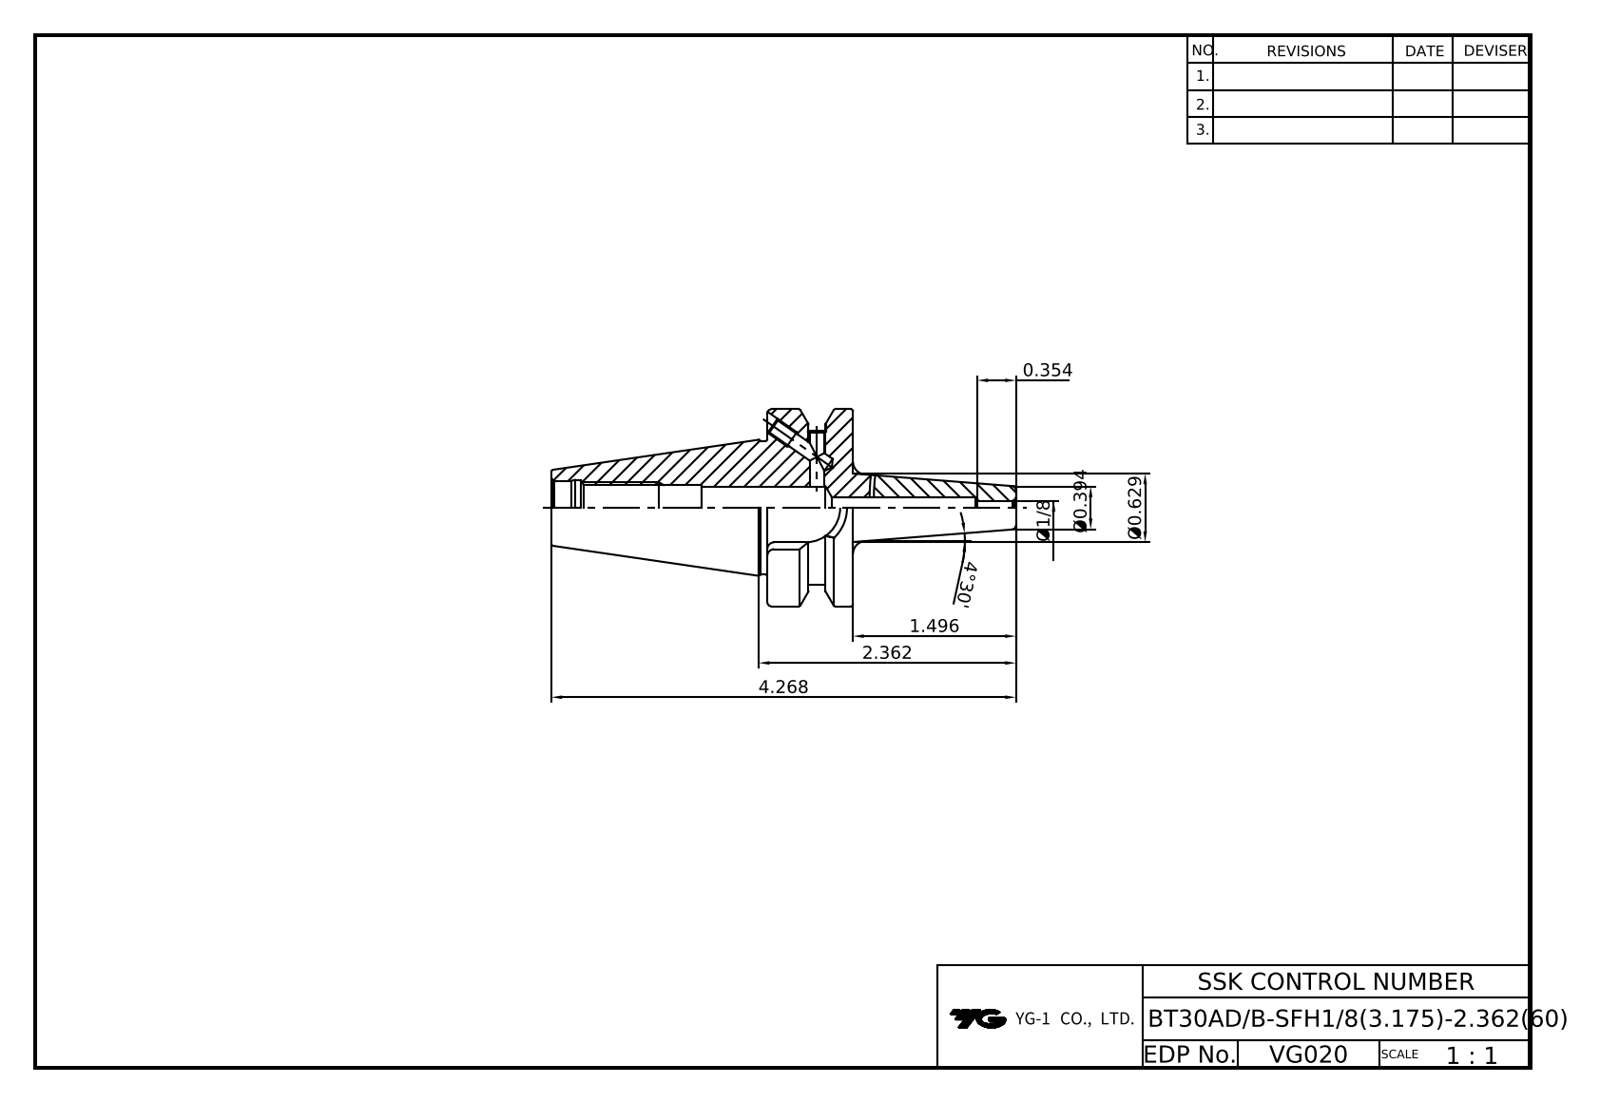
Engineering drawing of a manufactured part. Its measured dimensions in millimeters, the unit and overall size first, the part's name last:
Units: millimetres
Overall size (bounding box): 108.4 × 46 × 46
Round holes (diameter × count): ⌀3.17 ×1, ⌀5 ×1, ⌀10.11 ×1, ⌀12.5 ×1, ⌀13.1 ×1
Round bosses / shafts (diameter × count): ⌀46 ×1, ⌀31.2 ×1
Partial cylindrical surfaces — rounded edges, fillets, slot ends (radius × count): R8.05 ×1, R18.8 ×1
Main face-to-face distances: 20, 32.6, 16.1, 50.4, 70.4, 64, 13.6, 6.4, 60, 9.6
Volume: 51 946 mm³ · Surface area: 14 212 mm²
Bodies: 1 solid, 47 faces (15 planar, 13 cylindrical, 19 other)
Part name (STEP PRODUCT): LO-BT30-SFH3.175-2.36
STEP written by: Autodesk Inventor 2025 (AUTOMOTIVE_DESIGN)
